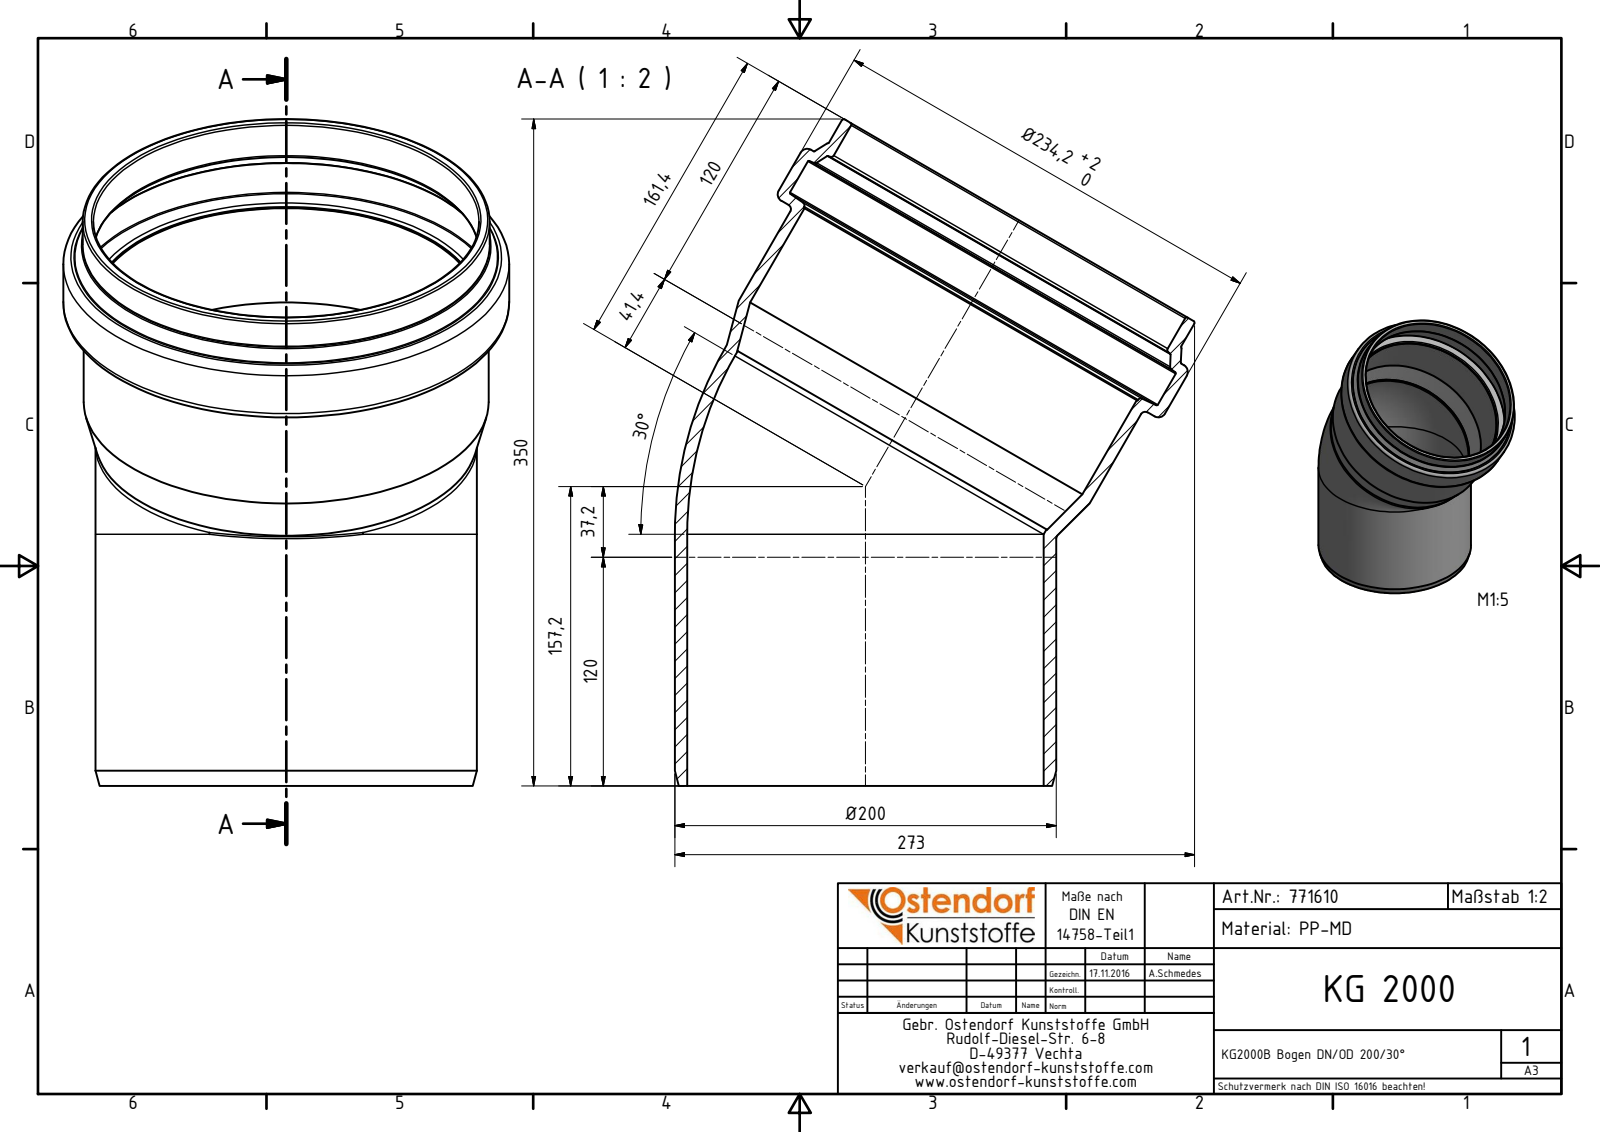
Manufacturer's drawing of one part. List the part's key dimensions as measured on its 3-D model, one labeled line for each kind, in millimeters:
Part name (STEP PRODUCT): 771610 KG2000B Bogen DN_OD 200_30°
STEP written by: Autodesk Inventor 2016 (AUTOMOTIVE_DESIGN)
Units: millimetres
Bodies: 1 solid, 42 faces (6 planar, 11 cylindrical, 25 other)
Overall size (bounding box): 350 × 273 × 234.2
Volume: 1 244 000 mm³ · Surface area: 427 320 mm²
Round holes (diameter × count): ⌀187.3 ×2, ⌀202.5 ×2, ⌀201.5 ×1, ⌀223 ×1
Round bosses / shafts (diameter × count): ⌀200.3 ×2, ⌀234.2 ×1, ⌀213.7 ×1, ⌀212.7 ×1
Main face-to-face distances: 53.6, 31, 22.6, 2.71, 28.29, 50.89, 79.77, 82.48, 110.77, 133.37
